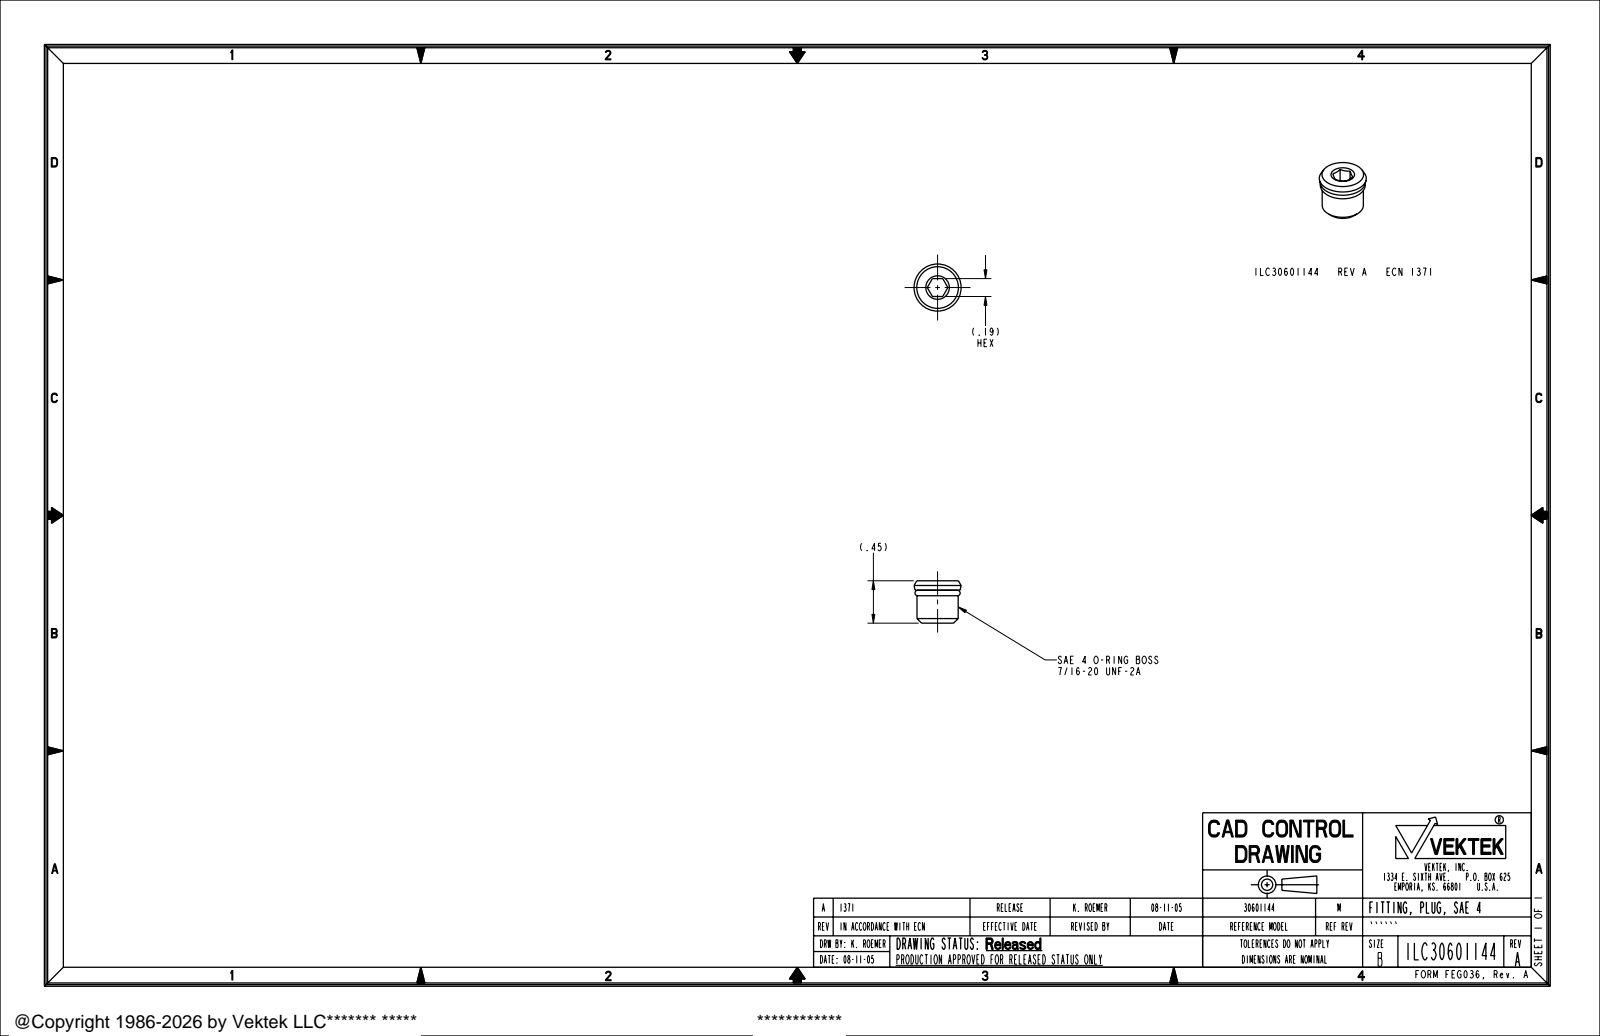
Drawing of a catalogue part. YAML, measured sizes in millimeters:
part_name: "ILC30601144"
step_written_by: "PRO/ENGINEER BY PARAMETRIC TECHNOLOGY CORPORATION, 2004290 (AUTOMOTIVE_DESIGN_CC2)"
units: millimeters
bodies: {solids: 1, faces: 24, planar: 10, cylindrical: 4, other: 10}
overall_size: [12.7, 12.7, 11.4]
volume: 1000
surface_area: 735
round_bosses_or_shafts:
  - {diameter: 11.1, count: 1}
face_to_face_distances: [11.4, 4.8, 6.9, 4.6, 2.5, 4.3, 8.9]
